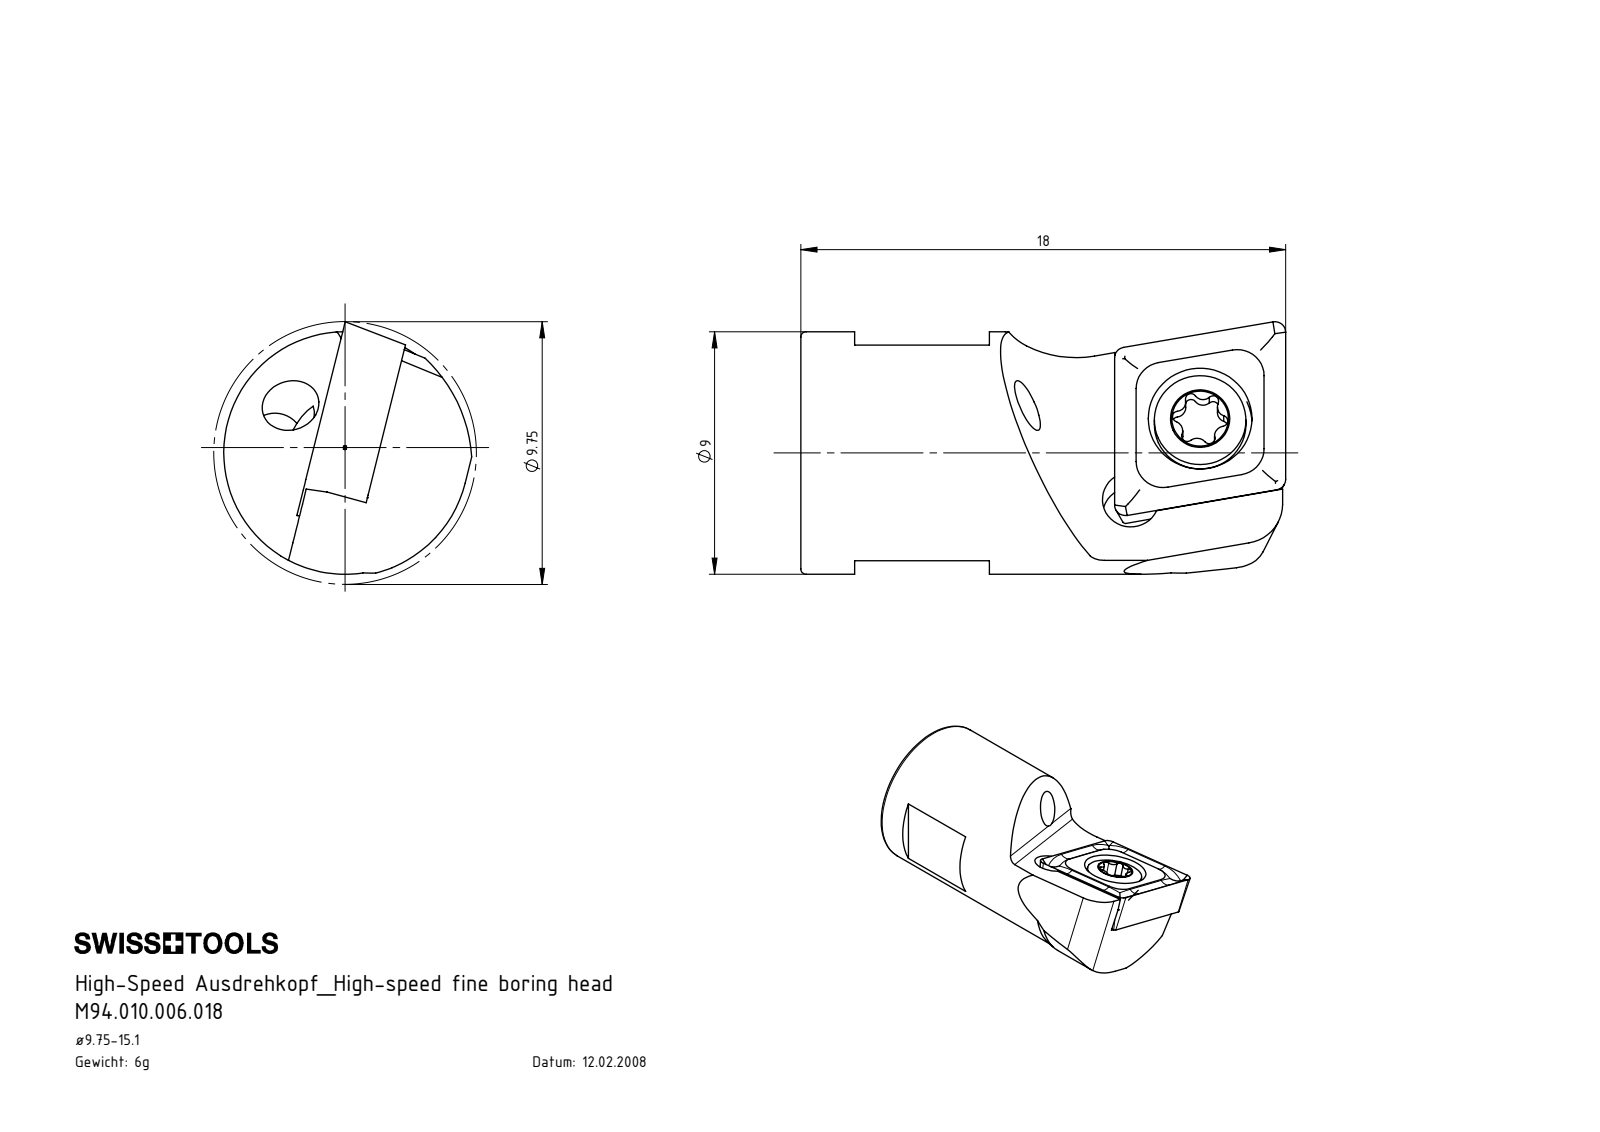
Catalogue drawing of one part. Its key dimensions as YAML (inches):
part_name: "HS5-A10.K11.018_D; HS5.A10.K11.018; WCA-ER2.001.005_B; CCMT060204"
step_written_by: "SolidWorks 2017 (AUTOMOTIVE_DESIGN)"
units: inches
bodies: {solids: 3, faces: 103, planar: 40, cylindrical: 26, other: 37}
overall_size: [0.709, 0.369, 0.363]
volume: 0.046
surface_area: 1.4
round_holes:
  - {diameter: 0.079, count: 1}
  - {diameter: 0.081, count: 1}
  - {diameter: 0.083, count: 1}
  - {diameter: 0.11, count: 1}
  - {diameter: 0.152, count: 1}
  - {diameter: 0.165, count: 1}
round_bosses_or_shafts:
  - {diameter: 0.354, count: 1}
  - {diameter: 0.134, count: 1}
  - {diameter: 0.098, count: 1}
partial_cylinders:
  - {radius: 0.008, count: 6}
  - {radius: 0.014, count: 5}
  - {radius: 0.014, count: 1}
  - {radius: 0.02, count: 1}
  - {radius: 0.059, count: 1}
  - {radius: 0.157, count: 1}
  - {radius: 0.181, count: 1}
  - {radius: 0.217, count: 1}
face_to_face_distances: [0.09, 0.315, 0.094, 0.463, 0.197, 0.079, 0.384, 0.276, 0.187, 0.058]
hole_center_spacings: [0.158]
